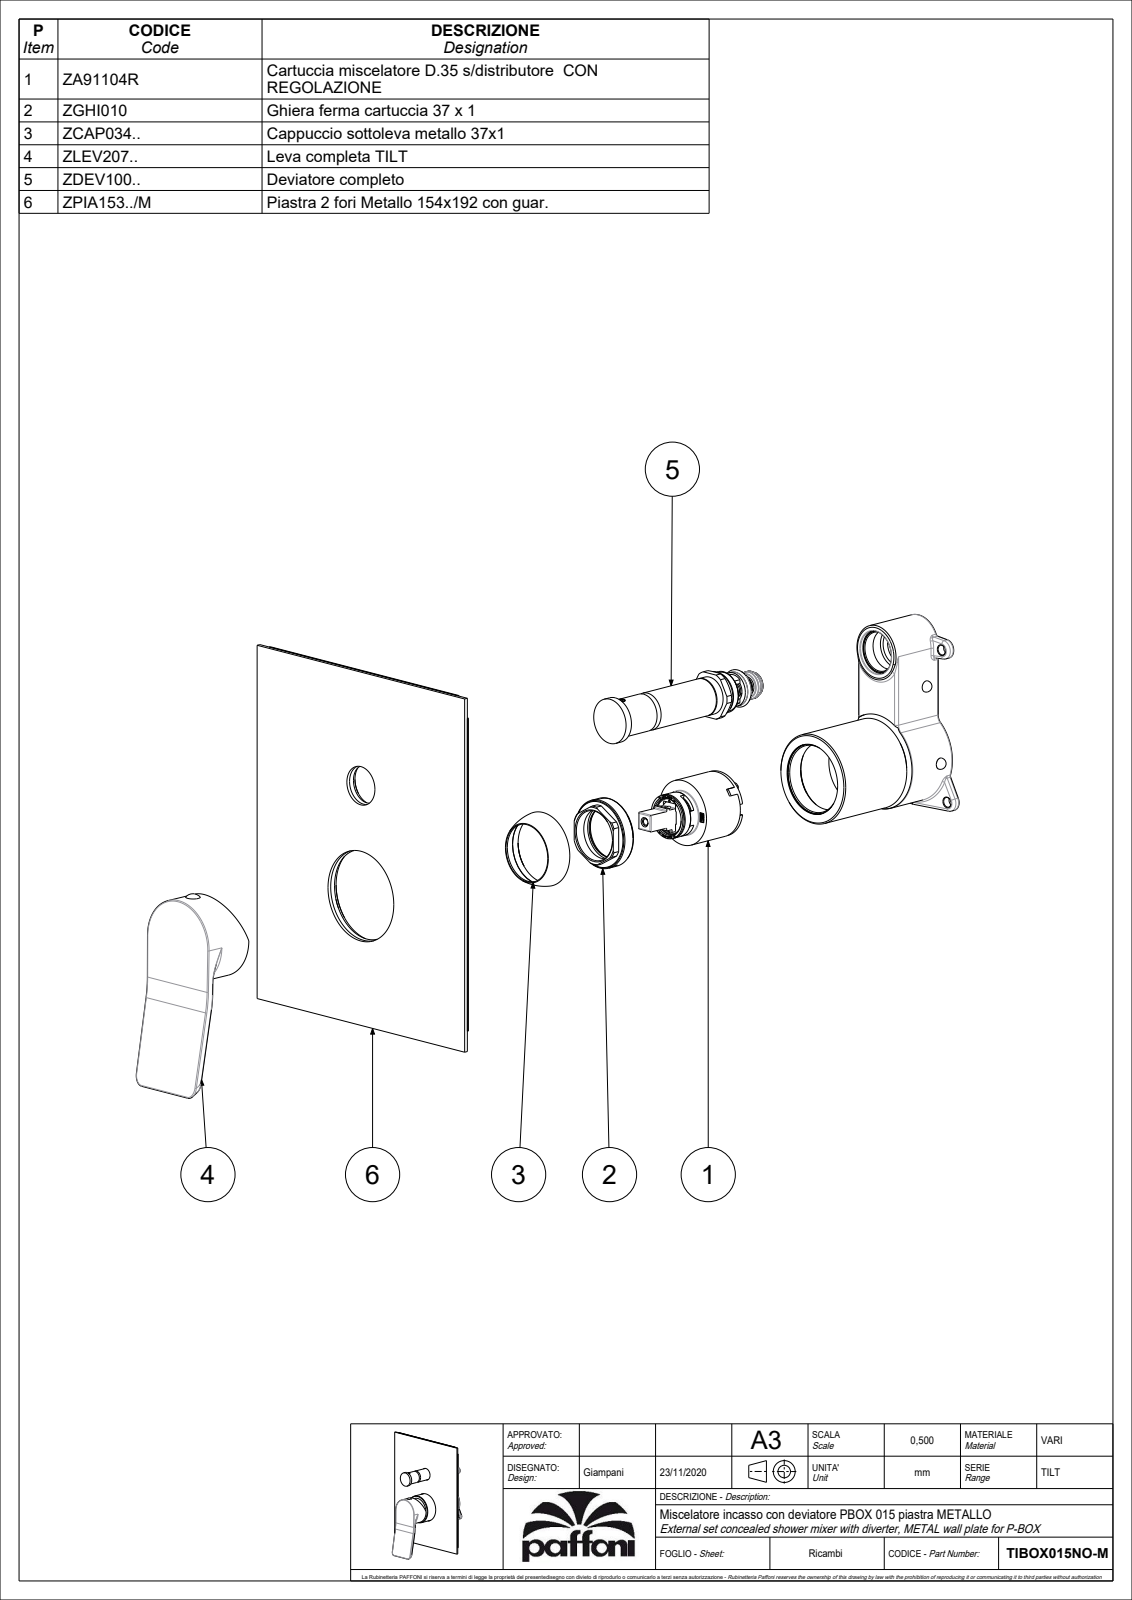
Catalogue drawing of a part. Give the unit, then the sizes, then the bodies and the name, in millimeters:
Units: millimetres
Overall size (bounding box): 201.33 × 154 × 63.05
Round holes (diameter × count): ⌀4 ×2, ⌀3 ×1, ⌀3.3 ×1, ⌀5 ×1, ⌀5.5 ×1, ⌀7.1 ×1, ⌀16 ×1, ⌀18.2 ×1, ⌀19.5 ×1, ⌀19.9 ×1, ⌀20.8 ×1, ⌀26.8 ×1
Round bosses / shafts (diameter × count): ⌀48.1 ×1, ⌀45.5 ×1, ⌀35 ×1, ⌀24 ×1, ⌀23.5 ×1, ⌀23.4 ×1, ⌀21.8 ×1, ⌀20 ×1
Partial cylindrical surfaces — rounded edges, fillets, slot ends (radius × count): R0.5 ×16, R0.15 ×11, R0.3 ×4, R1 ×2, R1.5 ×2, R5 ×2, R2.5 ×1, R6.5 ×1
Main face-to-face distances: 2, 4.01, 54.1, 52.1, 4, 50.1, 48.1, 22, 28.1, 5.5
Hole centre spacings: 13, 60
Volume: 126 518 mm³ · Surface area: 102 489 mm²
Bodies: 4 solids, 926 faces (573 planar, 210 cylindrical, 143 other)
Part name (STEP PRODUCT): TIBOX015NO-M
STEP written by: CREO PARAMETRIC BY PTC INC, 2020044 (CONFIG_CONTROL_DESIGN)
